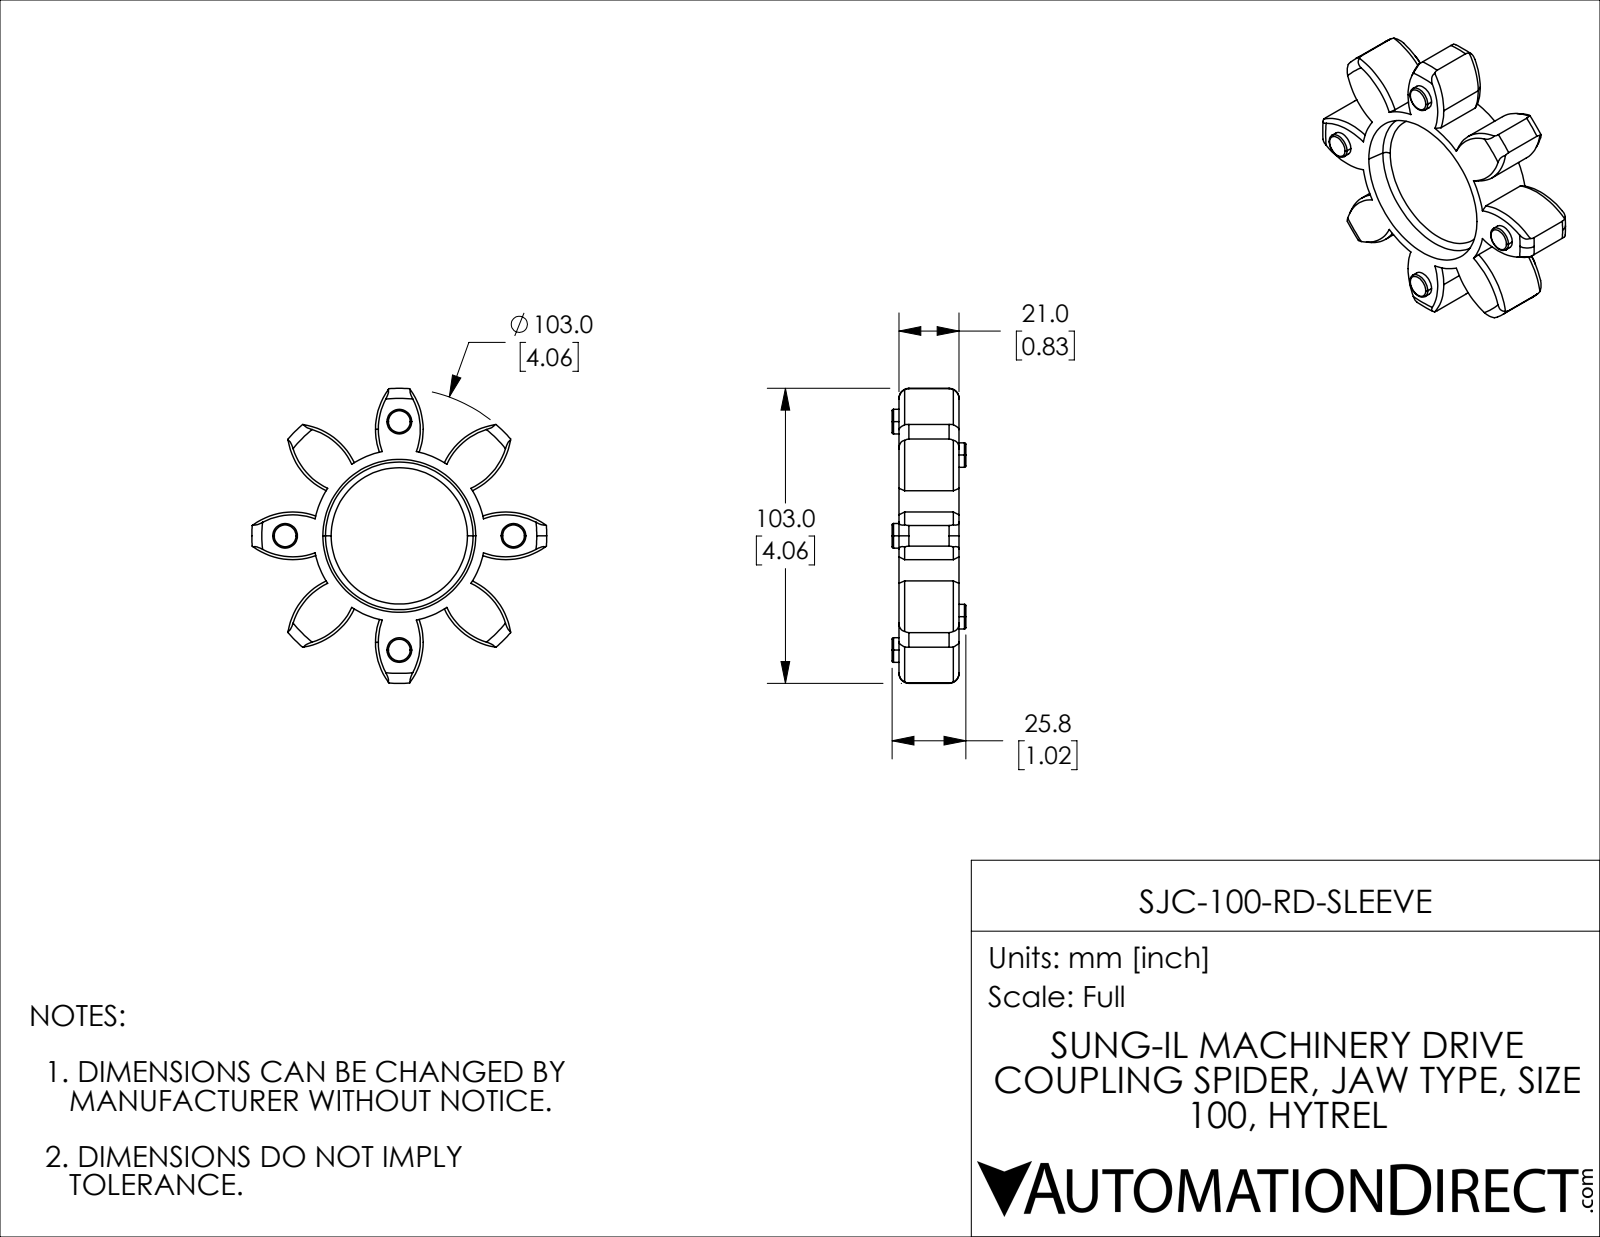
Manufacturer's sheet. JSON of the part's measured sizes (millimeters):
{"part_name": "SJC-100-RD-SLEEVE", "step_written_by": "SolidWorks 2021 (CONFIG_CONTROL_DESIGN)", "units": "millimeters", "bodies": {"solids": 1, "faces": 141, "planar": 12, "cylindrical": 51, "other": 78}, "overall_size": [103, 103, 25.8], "volume_mm3": 79152, "surface_area_mm2": 23000, "round_bosses_or_shafts": [[8.6, 8]], "partial_cylinders_radius": [[23.73, 8], [30, 1], [51.5, 1]], "face_to_face_distances": [7.7, 13.3, 21, 5.6, 2.4, 10.1, 15.7, 23.4, 25.8]}
